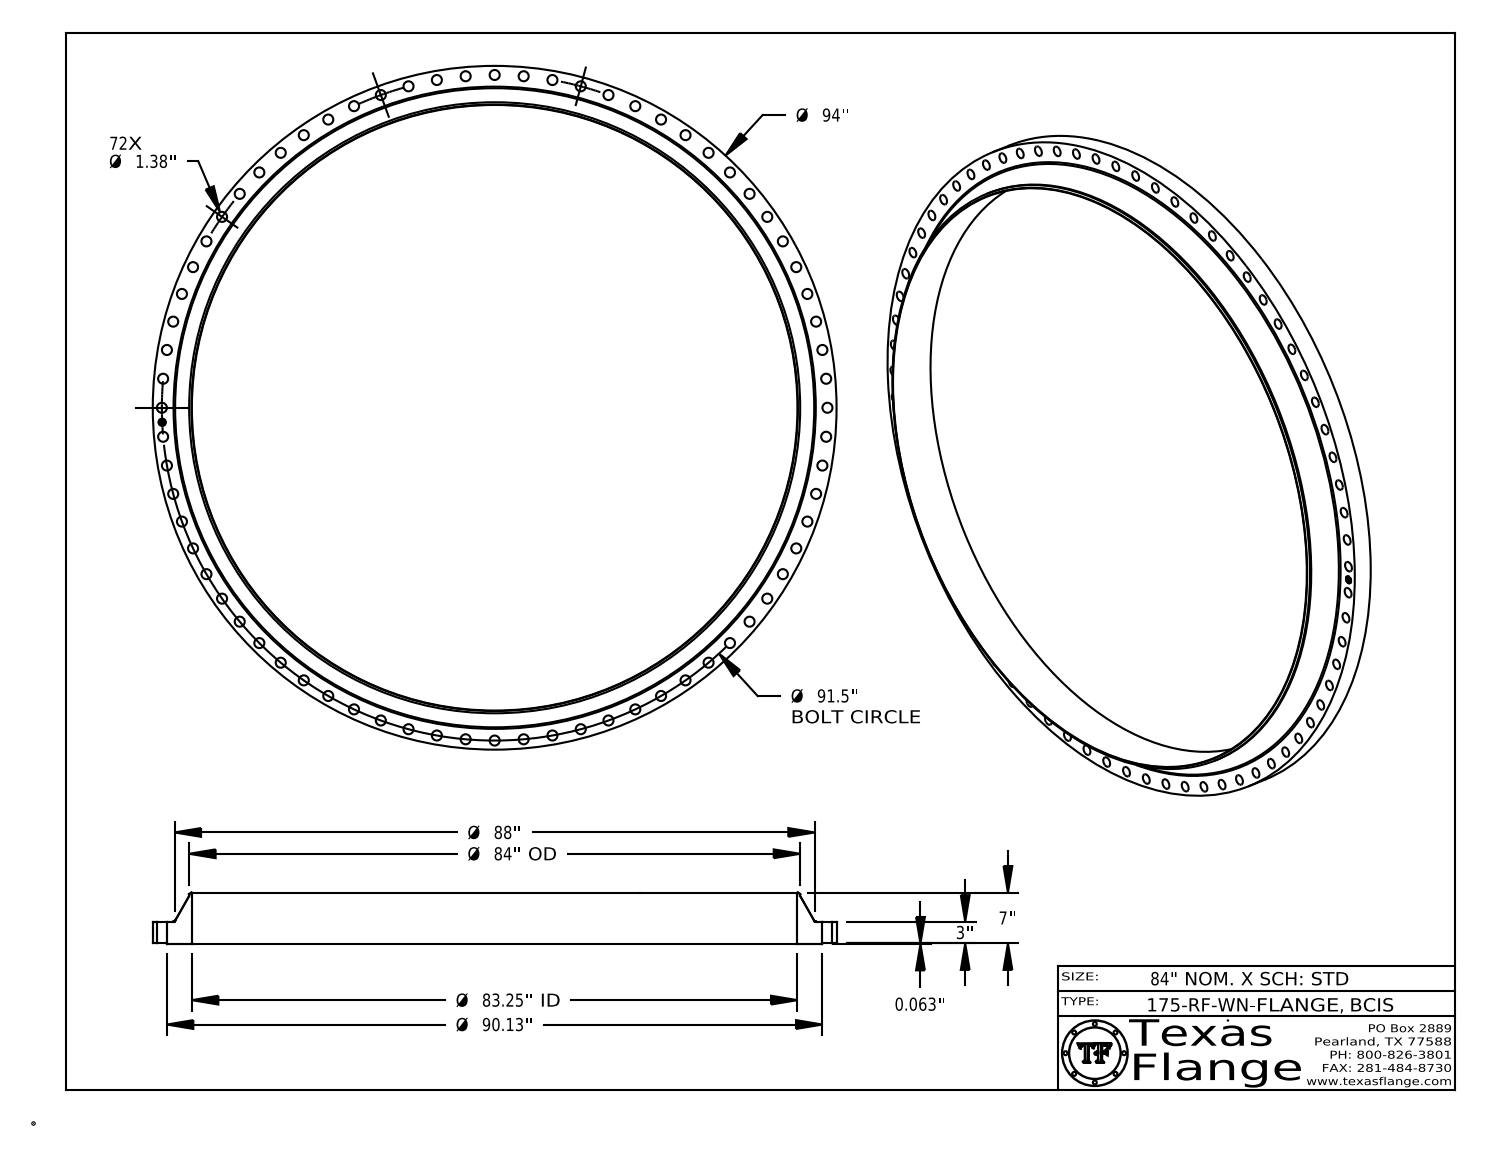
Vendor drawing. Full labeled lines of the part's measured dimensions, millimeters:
Part name (STEP PRODUCT): 175-RF-WN, BCIS
STEP written by: CATIA V5 STEP AP214 (AUTOMOTIVE_DESIGN)
Units: millimetres
Bodies: 1 solid, 619 faces (369 planar, 244 cylindrical, 6 other)
Overall size (bounding box): 2387.6 × 2387.6 × 179.4
Volume: 91 030 000 mm³ · Surface area: 4 578 000 mm²
Round holes (diameter × count): ⌀35.1 ×72, ⌀25.4 ×1, ⌀2114.6 ×1
Round bosses / shafts (diameter × count): ⌀1.5 ×8, ⌀2387.6 ×1, ⌀2289.3 ×1, ⌀2133.6 ×1, ⌀20 ×1
Main face-to-face distances: 77.8, 1.6, 76.2, 179.4, 177.8, 101.6, 0.4, 77.4, 75.8, 102
Hole centre spacings: 1162.1, 303.4, 101.4, 202.6, 503, 1162.1, 403.6, 794.9
